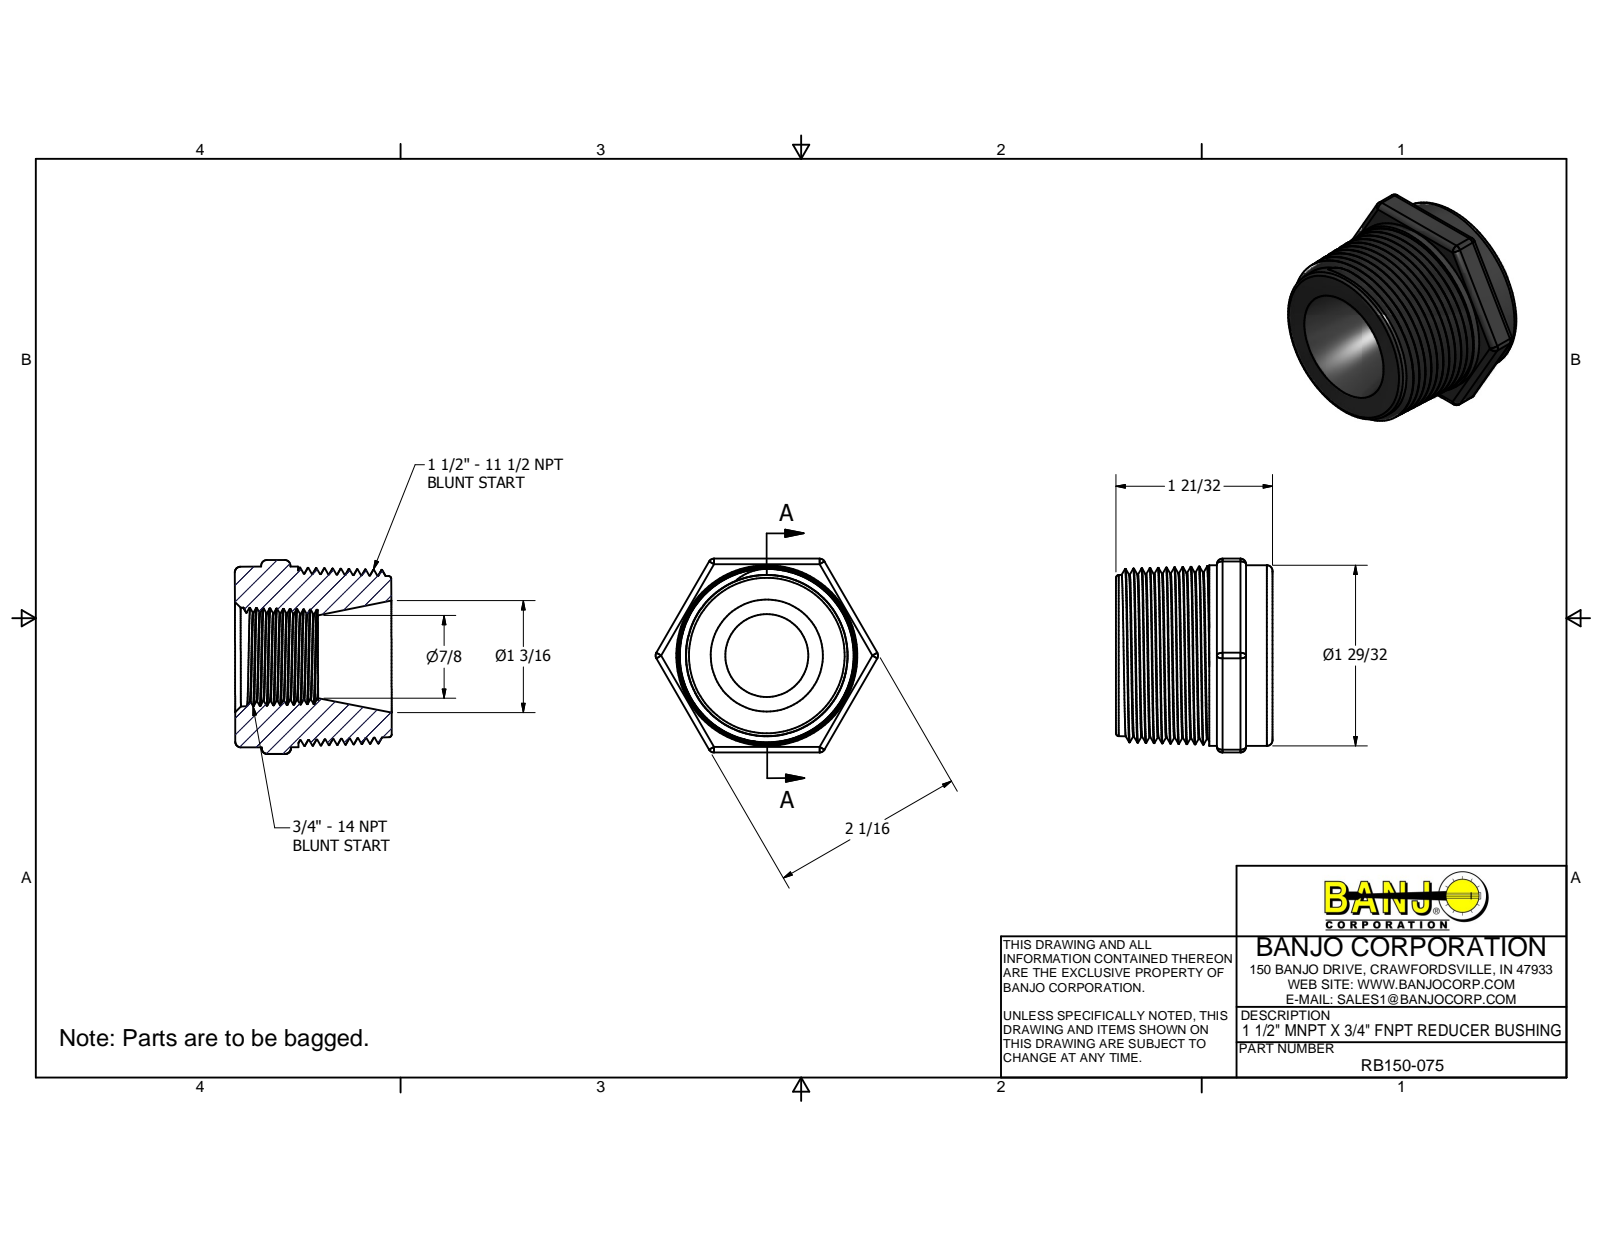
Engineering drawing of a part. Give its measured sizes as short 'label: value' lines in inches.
name: RB150-075
written by: Autodesk Inventor 2014 (AUTOMOTIVE_DESIGN)
unit: in
bodies: 1 solid, 83 faces (12 planar, 22 cylindrical, 49 other)
size: 2.36 × 2.06 × 1.66
volume: 3.336 in³; area: 25.8 in²
bosses: 1× ⌀1.92
rounds: 18× R0.06, 1× R0.313, 1× R0.493
face distances: 1.66, 2.06, 0.28, 0.59, 0.31, 1.38, 1.07, 0.67, 0.39, 0.08
